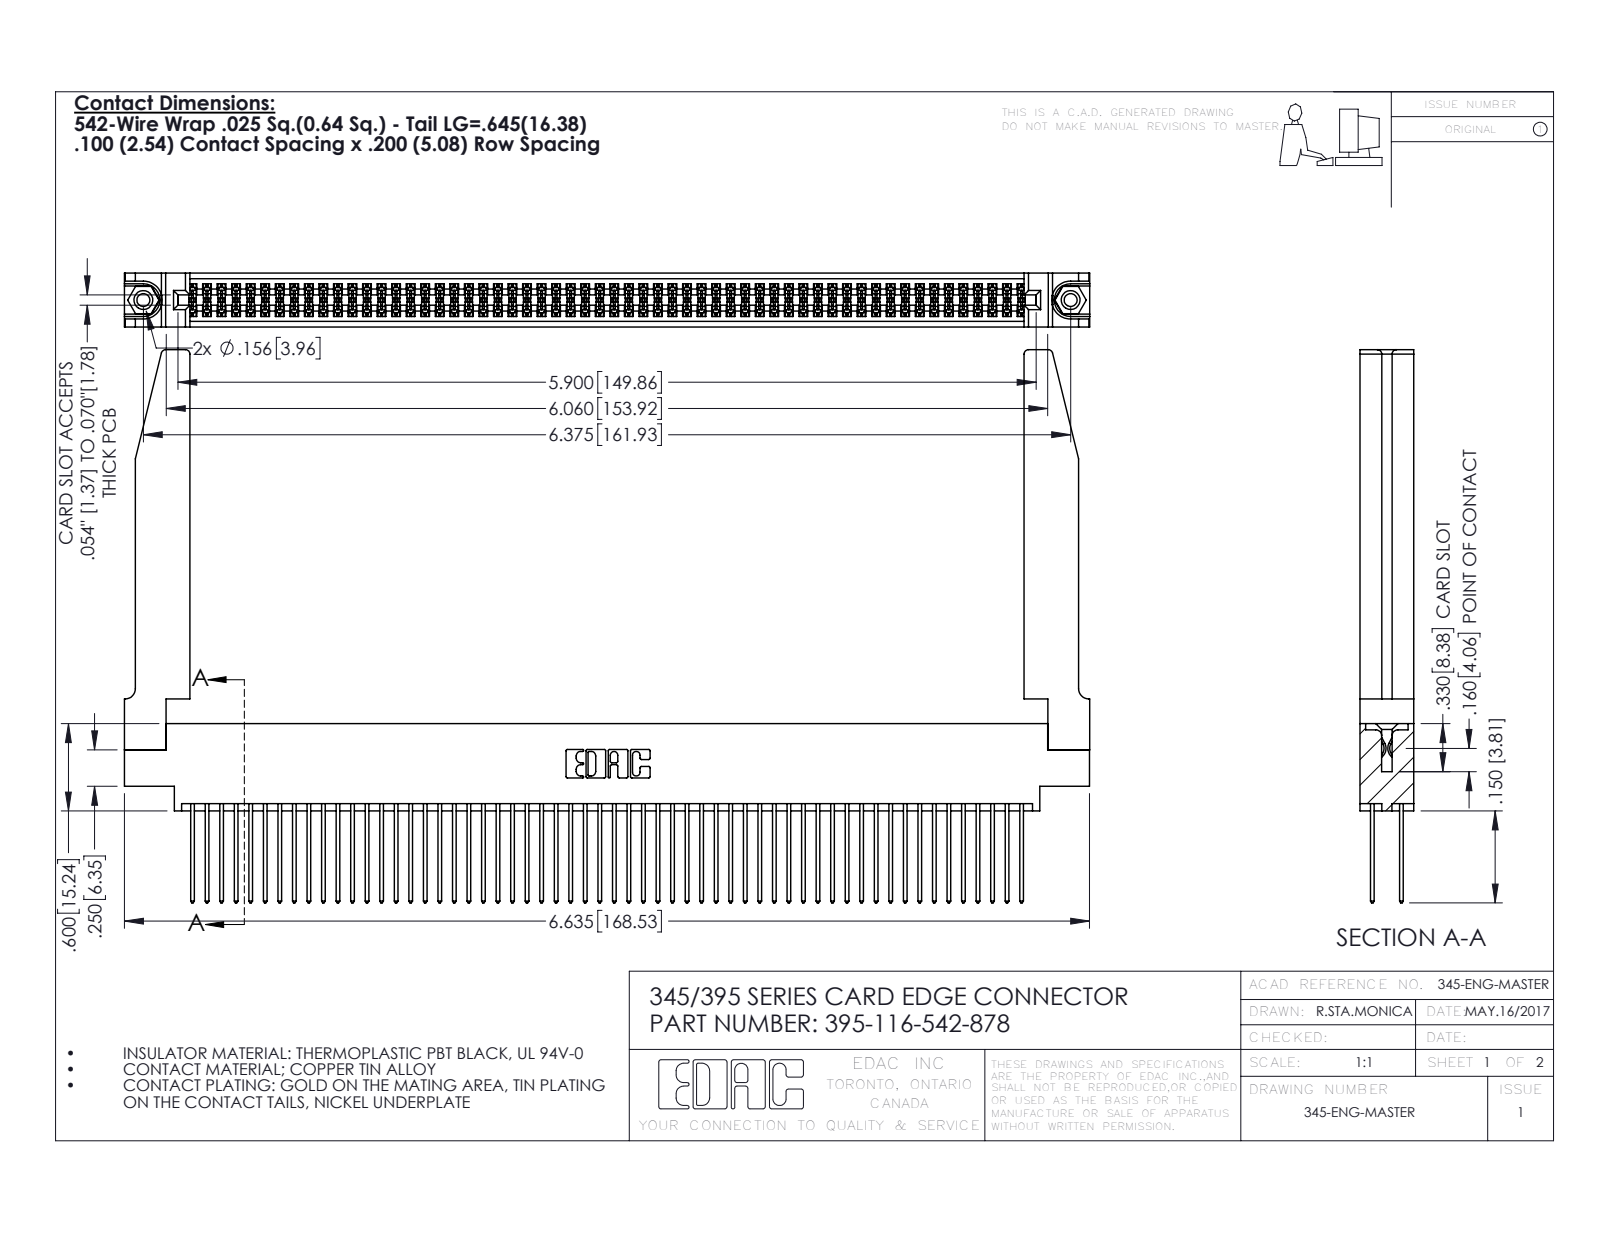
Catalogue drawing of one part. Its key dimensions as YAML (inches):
part_name: "345-220-078_345-220-078; 345 Part_0.170 Offset - 0.156 Dia-TH; 395-116-542-878; 345-250-001_345-250-001-102 (+1 more)"
step_written_by: "SolidWorks 2016 (CONFIG_CONTROL_DESIGN)"
units: inches
bodies: {solids: 121, faces: 6164, planar: 4054, cylindrical: 2058, other: 52}
overall_size: [6.636, 3.802, 0.37]
volume: 1.508
surface_area: 54.05
round_holes:
  - {diameter: 0.089, count: 2}
  - {diameter: 0.125, count: 2}
  - {diameter: 0.156, count: 2}
  - {diameter: 0.064, count: 1}
round_bosses_or_shafts:
  - {diameter: 0.155, count: 2}
partial_cylinders:
  - {radius: 0.006, count: 174}
  - {radius: 0.01, count: 116}
  - {radius: 0.01, count: 22}
  - {radius: 0.03, count: 8}
  - {radius: 0.007, count: 6}
  - {radius: 0.031, count: 6}
  - {radius: 0.026, count: 3}
  - {radius: 0.014, count: 2}
face_to_face_distances: [0.072, 0.298, 0.37, 0.098, 0.272, 0.025, 0.2, 0.225, 0.175, 0.15]
hole_center_spacings: [0.27, 6.139, 6.375]
